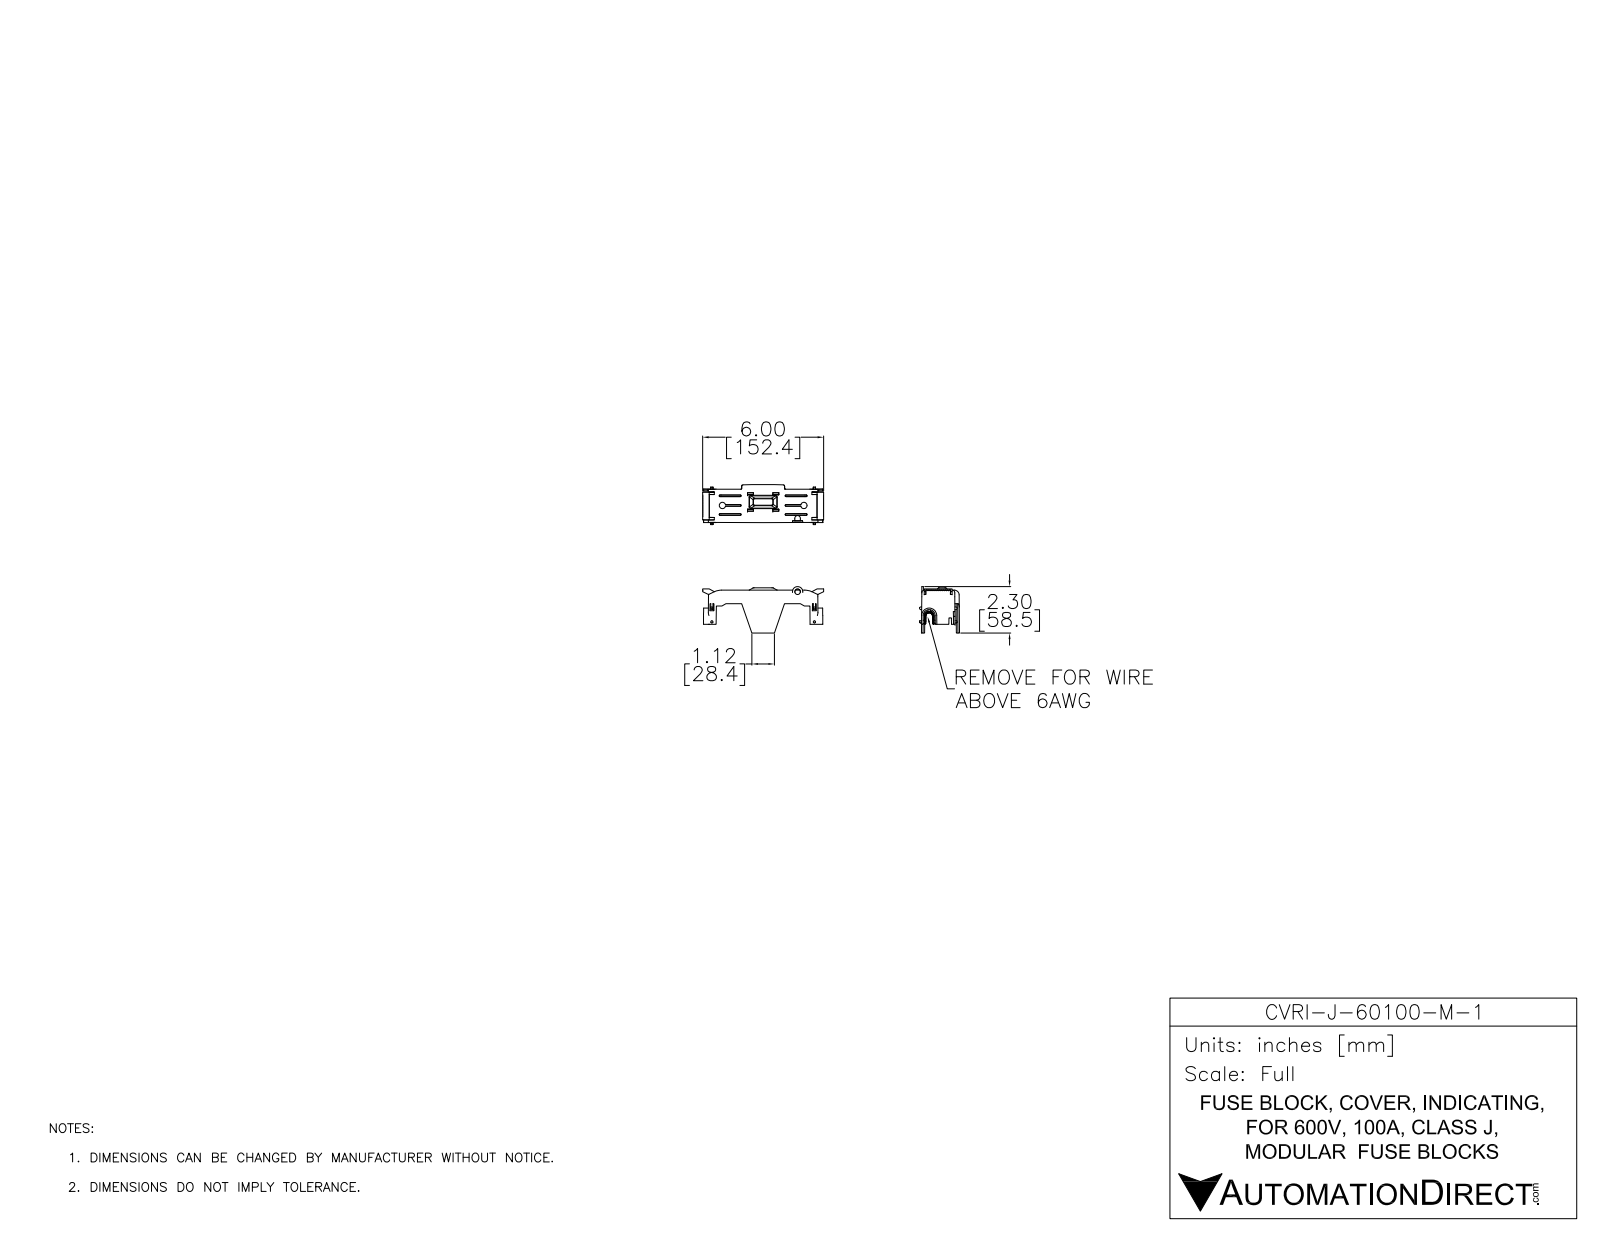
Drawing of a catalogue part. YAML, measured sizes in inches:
part_name: "CVRI-J-60100-M-1"
step_written_by: "SolidWorks 2017 (AUTOMOTIVE_DESIGN)"
units: inches
bodies: {solids: 1, faces: 1410, planar: 917, cylindrical: 102, other: 391}
overall_size: [5.979, 2.304, 1.984]
volume: 2.55
surface_area: 70.01
partial_cylinders:
  - {radius: 0.039, count: 19}
  - {radius: 0.118, count: 14}
  - {radius: 0.031, count: 6}
  - {radius: 0.059, count: 4}
  - {radius: 0.01, count: 2}
  - {radius: 0.02, count: 2}
  - {radius: 0.138, count: 2}
  - {radius: 0.169, count: 2}
face_to_face_distances: [0.079, 0.217, 0.138, 0.295, 0.118, 0.347, 0.197, 0.236, 0.14, 0.061]
